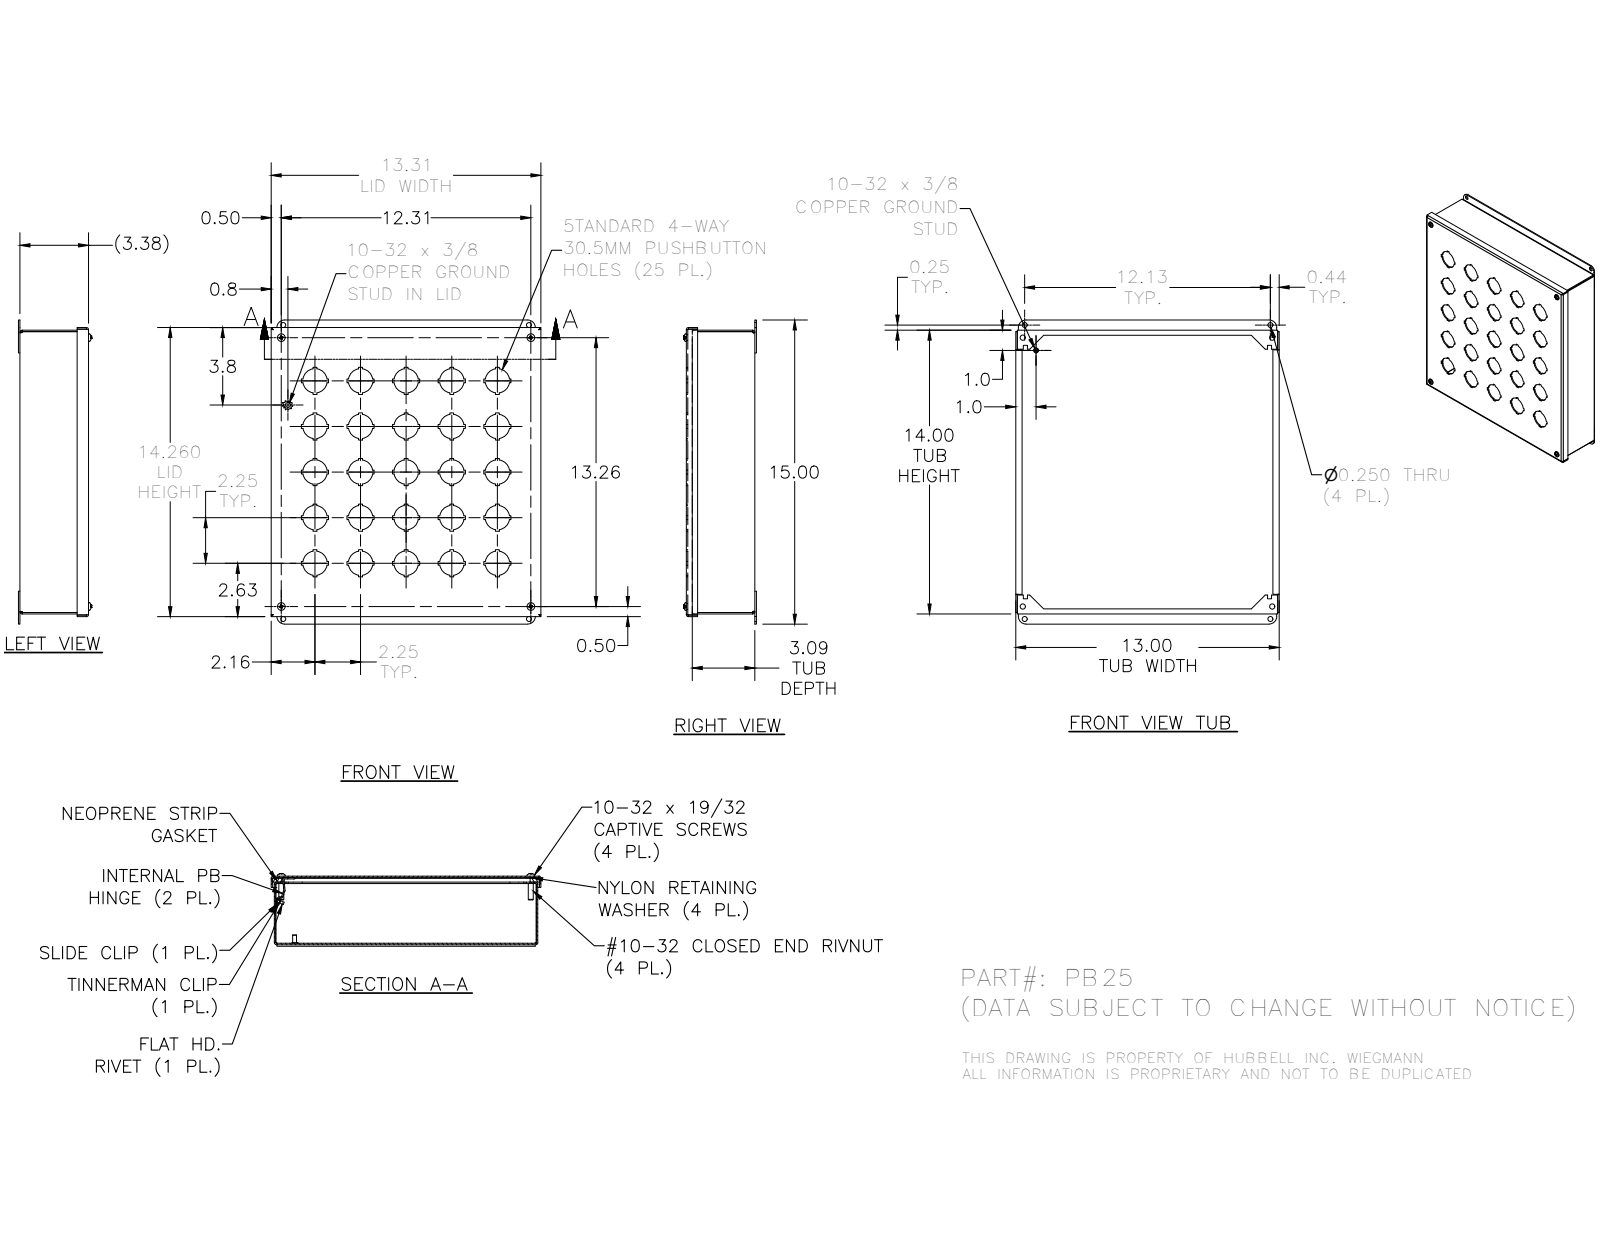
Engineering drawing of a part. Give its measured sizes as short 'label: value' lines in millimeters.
name: PB25LID; 3285; 39077; 316235 (+8 more)
written by: Autodesk Inventor 2016 (AUTOMOTIVE_DESIGN)
unit: mm
bodies: 25 solids, 1021 faces (663 planar, 244 cylindrical, 114 other)
size: 381 × 338.07 × 91.13
volume: 809 626 mm³; area: 829 840 mm²
holes: 25× ⌀30.48, 4× ⌀3.96, 4× ⌀4.98, 4× ⌀6.35, 4× ⌀6.53, 4× ⌀7.06, 4× ⌀7.14, 4× ⌀7.95, 2× ⌀3.56
bosses: 6× ⌀4.83, 4× ⌀11.51, 4× ⌀10.31, 4× ⌀9.47, 4× ⌀6.3, 3× ⌀6.35, 1× ⌀3.17
rounds: 12× R0.79, 12× R2.67, 8× R1.78, 6× R4.78, 4× R2.27, 4× R2.29, 4× R9.53, 3× R0.8
face distances: 1.88, 84.07, 85.95, 82.19, 328.32, 353.72, 7.46, 76.61, 78.49, 5.58
hole spacings: 127.79, 57.15, 80.82, 180.72, 114.3, 206.06, 171.45, 161.64
